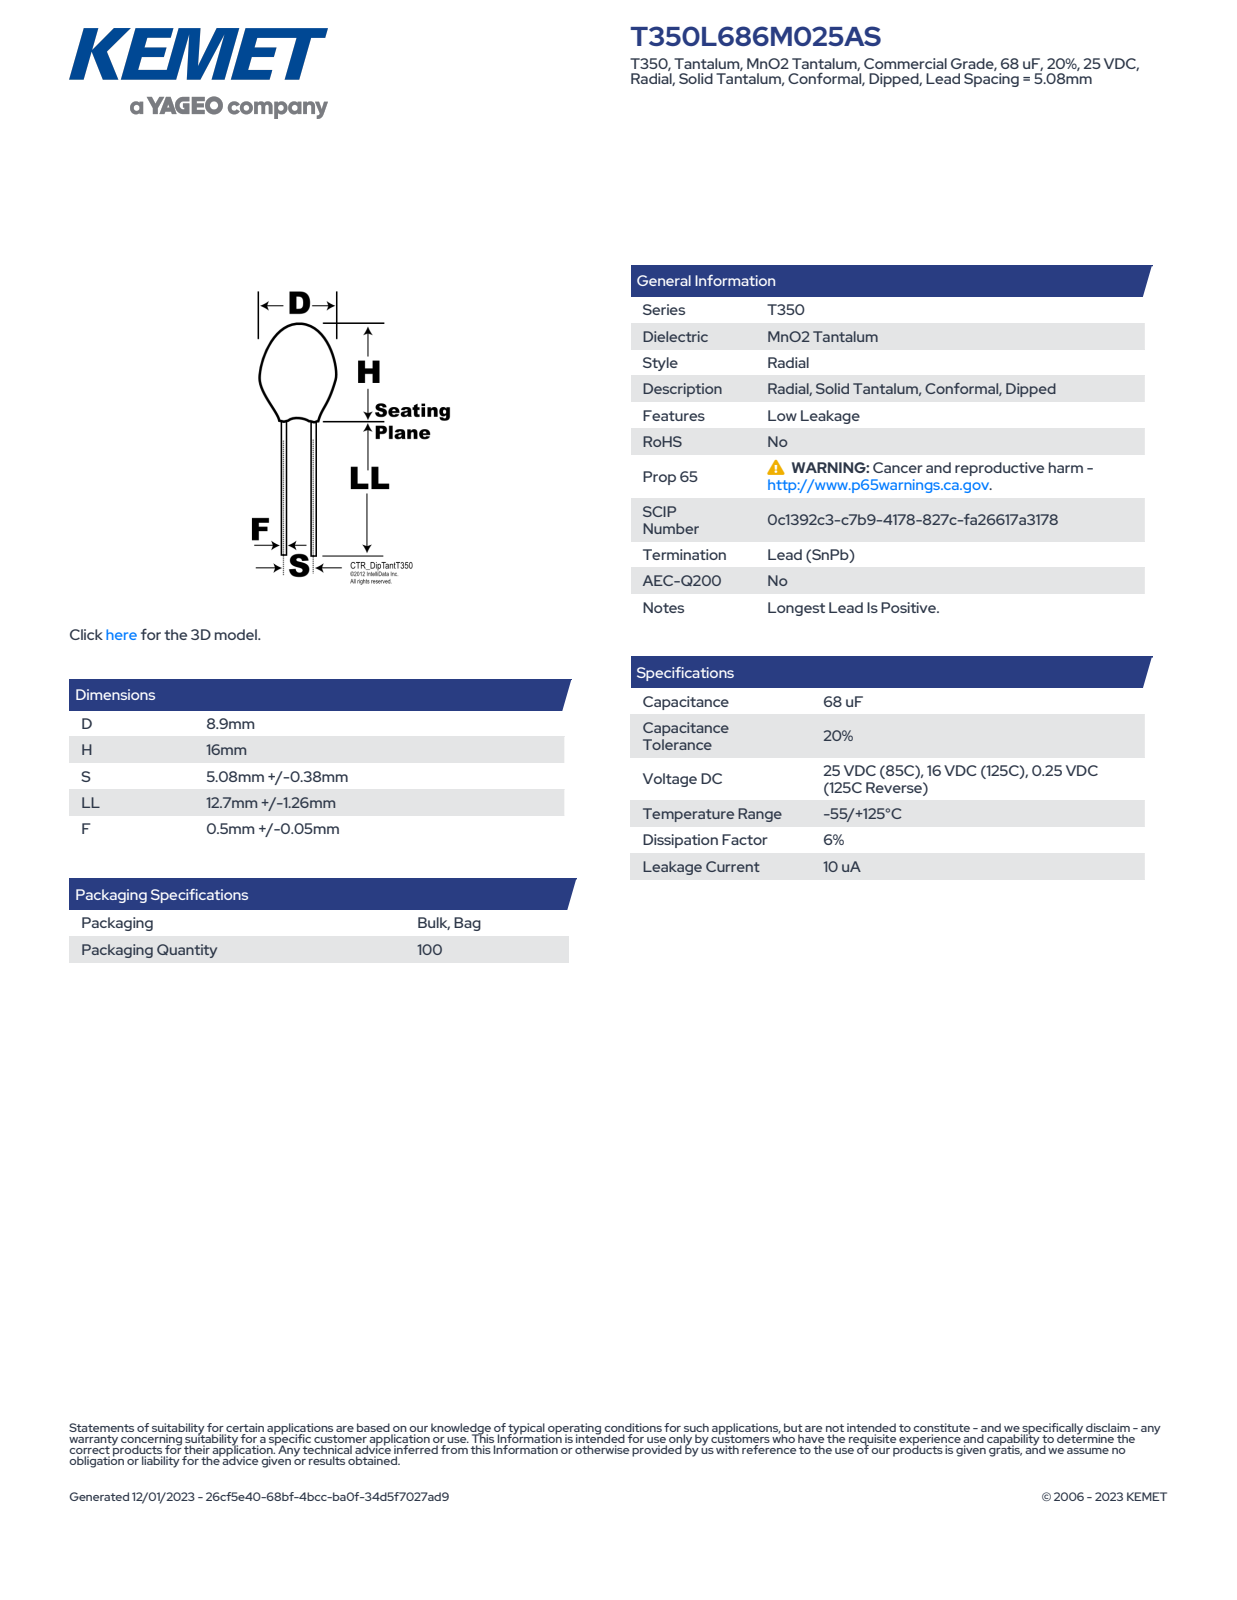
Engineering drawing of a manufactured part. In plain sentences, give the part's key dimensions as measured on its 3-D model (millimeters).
The part is named "CTR_T350_D8.9H16S5.08LL13.96F0.55". Its 3-D file was written by "SolidWorks 2014 (AUTOMOTIVE_DESIGN)". It is 1 solid with 73 faces: 26 planar, 10 cylindrical and 37 other. Overall it measures 29.96 by 8.9 by 8.9 millimeters. Its volume is 803 cubic millimeters and its surface area 504 square millimeters. Round bosses or shafts: 2 of diameter 0.55, 1 of diameter 8.9. Partial cylindrical surfaces (rounded edges, fillets, slot ends): 1 of radius 4.44. The main face-to-face distances are 16, 13.96, 29.96, 22.57, 8.61, 7.39, 21.56, 7.6, 1.01, 8.4.
